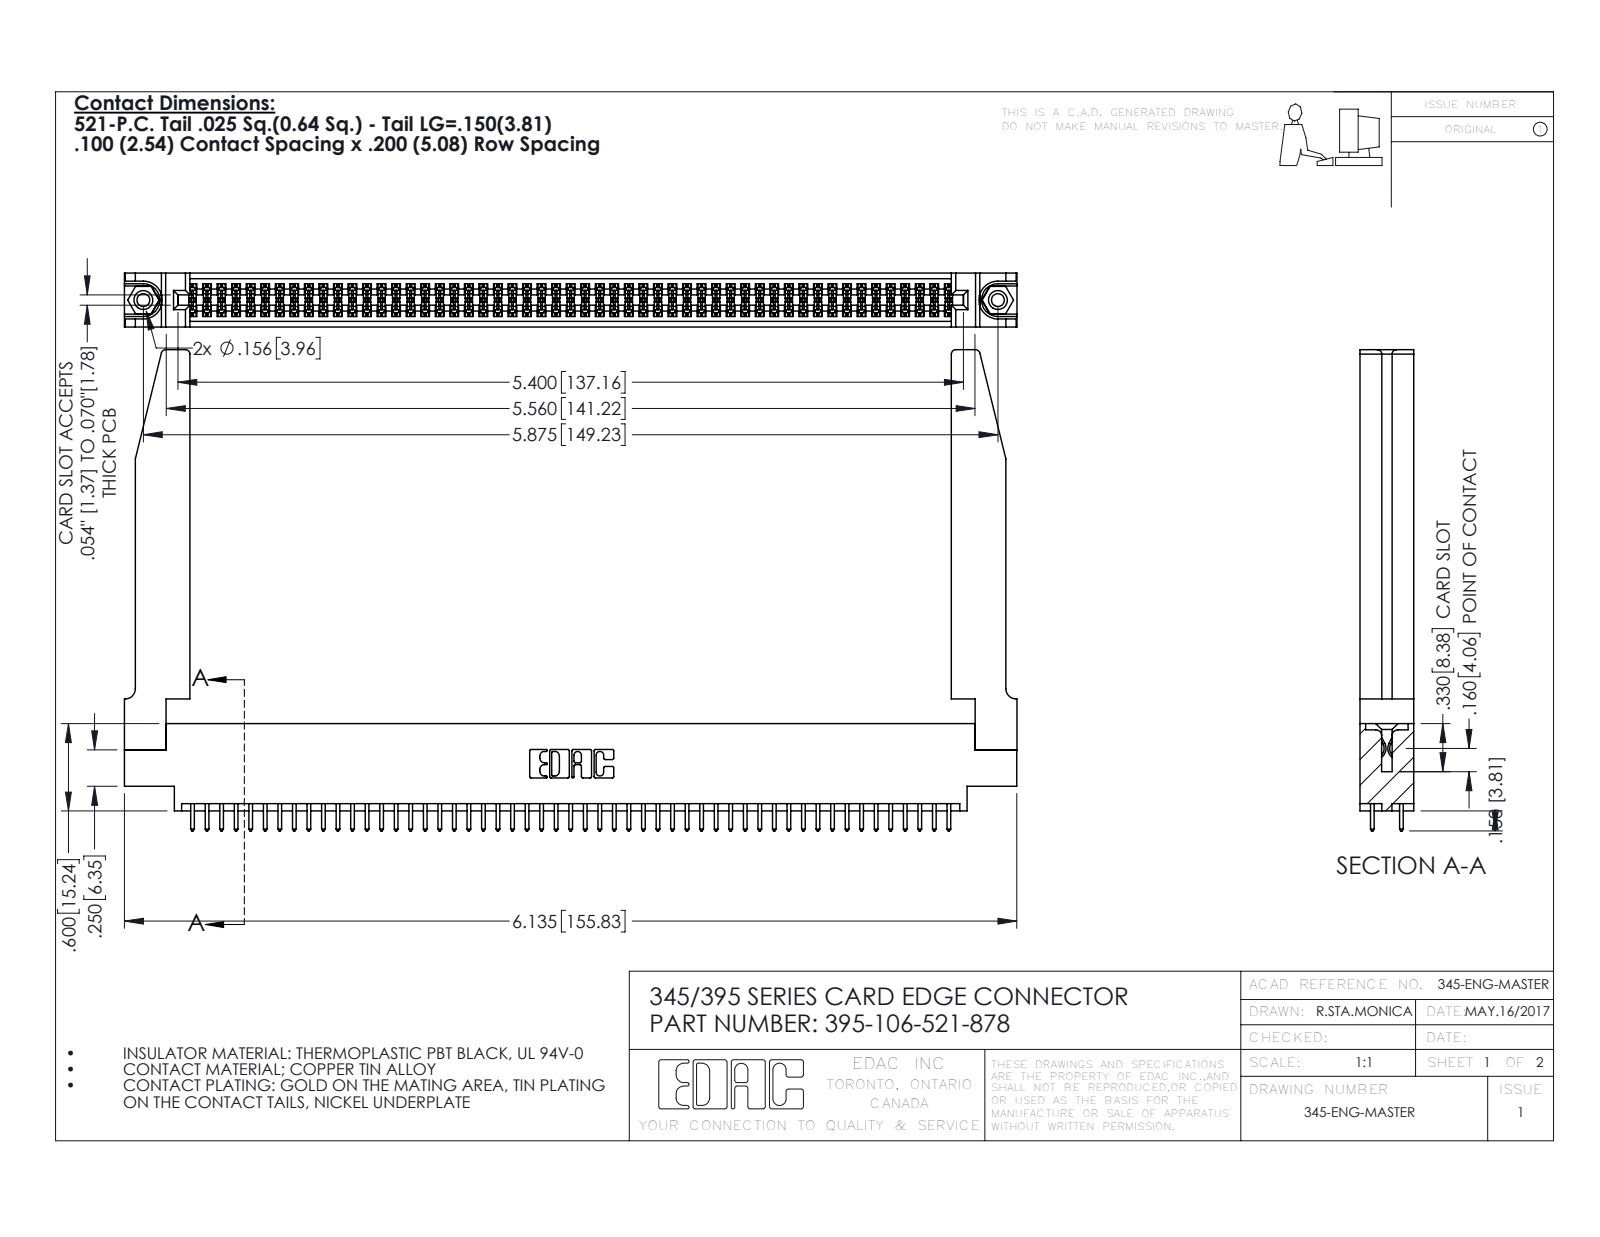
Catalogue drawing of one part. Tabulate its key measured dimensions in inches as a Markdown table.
| quantity | value |
| --- | --- |
| part name | 395-106-521-878; 345-292-001_345-293-121; 345-220-078_345-220-078; 345-250-001_345-250-001-102 (+1 more) |
| STEP written by | SolidWorks 2016 (CONFIG_CONTROL_DESIGN) |
| units | inches |
| bodies | 111 solids, 5664 faces (3724 planar, 1888 cylindrical, 52 other) |
| overall size | 6.136 × 3.307 × 0.37 |
| volume | 1.395 in³ |
| surface area | 45.28 in² |
| round holes (diameter × count) | 0.089 × 2, 0.125 × 2, 0.156 × 2, 0.064 × 1 |
| round bosses / shafts (diameter × count) | 0.155 × 2 |
| partial cylindrical surfaces (radius × count) | 0.006 × 159, 0.01 × 106, 0.01 × 22, 0.03 × 8, 0.007 × 6, 0.031 × 6, 0.026 × 3, 0.014 × 2 |
| main face-to-face distances | 0.072, 0.37, 0.298, 0.098, 0.272, 0.025, 0.2, 0.225, 0.175, 0.148 |
| hole center spacings | 0.27, 5.639, 5.875 |
